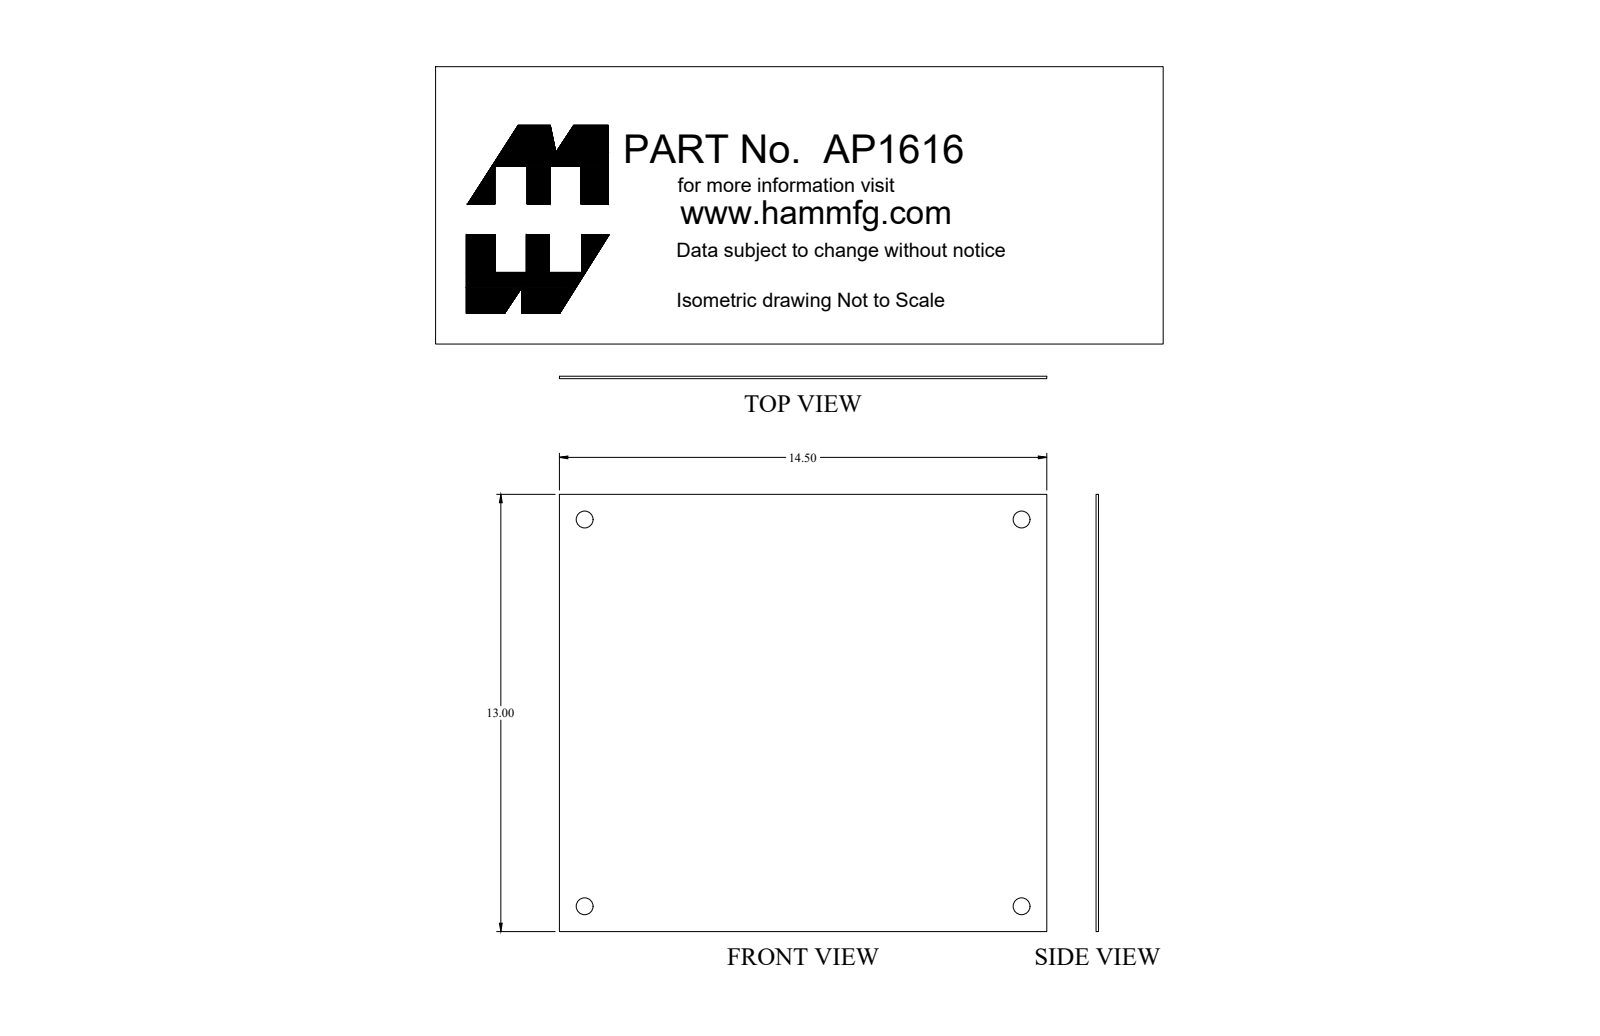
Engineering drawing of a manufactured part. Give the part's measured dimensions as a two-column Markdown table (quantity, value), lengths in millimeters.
| quantity | value |
| --- | --- |
| part name | AP1616_Default |
| STEP written by | SolidWorks 2019 (CONFIG_CONTROL_DESIGN) |
| units | millimeters |
| bodies | 1 solid, 14 faces (6 planar, 8 cylindrical, 0 other) |
| overall size | 368.3 × 330.2 × 1.8 |
| volume | 221 600 mm³ |
| surface area | 245 000 mm² |
| round holes (diameter × count) | 12.7 × 4 |
| main face-to-face distances | 1.8, 330.2, 368.3 |
| hole center spacings | 292.1, 330.2, 440.9 |
